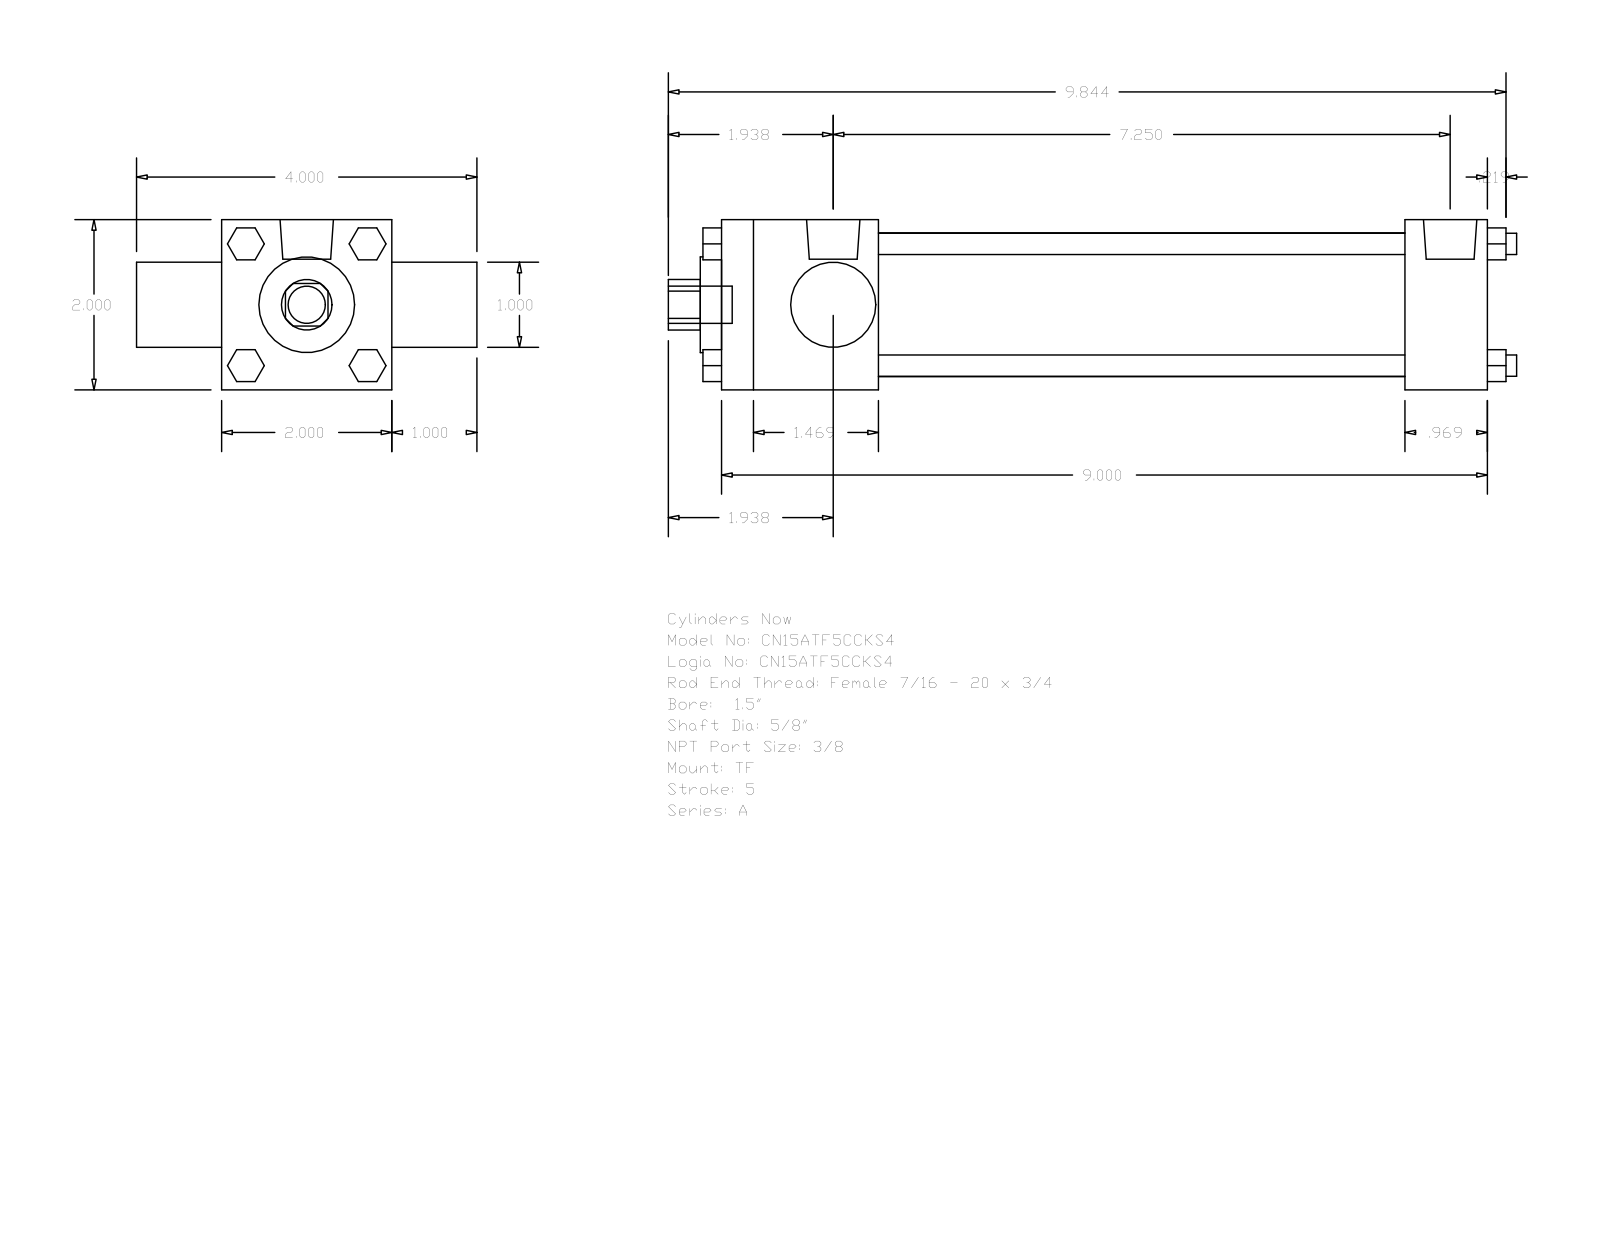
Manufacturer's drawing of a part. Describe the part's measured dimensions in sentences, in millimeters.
The part is named "A_TF__0150_0.625". Its 3-D file was written by "GSSL Pune (CONFIG_CONTROL_DESIGN)". It is 0 solids with 120 faces: 92 planar, 28 cylindrical and 0 other. Overall it measures 253.21 by 101.6 by 50.8 millimeters. Round holes: 1 of diameter 15.88, 1 of diameter 25.4, 1 of diameter 28.57, 1 of diameter 42.93. Round bosses or shafts: 4 of diameter 6.35, 3 of diameter 5.56, 2 of diameter 15.93, 1 of diameter 11.11. Partial cylindrical surfaces (rounded edges, fillets, slot ends): 1 of radius 7.54. The main face-to-face distances are 50.8, 228.59, 25.4, 76.2, 46.83, 203.99, 157.16, 181.76, 24.6, 9.52.
